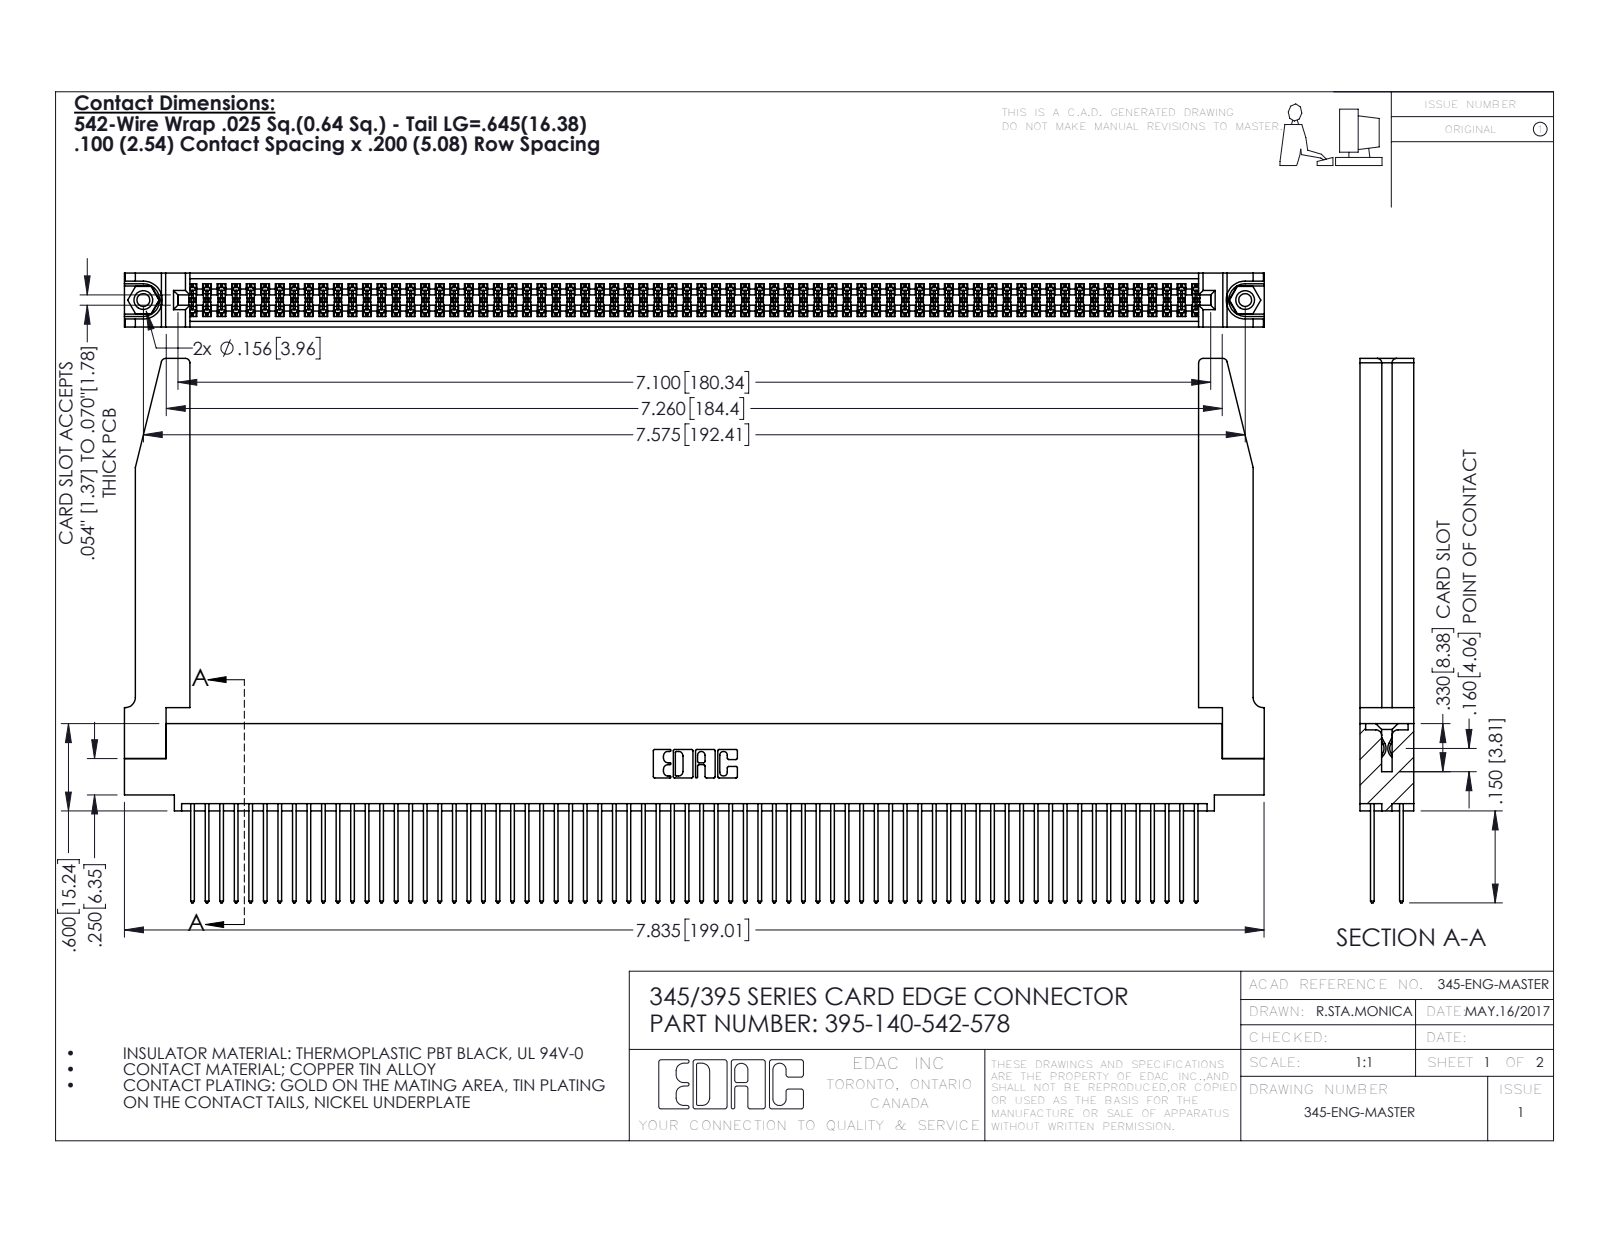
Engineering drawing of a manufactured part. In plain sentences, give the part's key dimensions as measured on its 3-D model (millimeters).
The part is named "345-220-078_345-220-078; 345 Part_0.110 Offset - 0.156 Dia-TH; 345-250-001_345-250-001-102; 345-292-001_345-293-142 (+1 more)". Its 3-D file was written by "SolidWorks 2016 (CONFIG_CONTROL_DESIGN)". It is 145 solids with 7364 faces: 4846 planar, 2466 cylindrical and 52 other. Overall it measures 199 by 95 by 9.4 millimeters. Its volume is 27 940 cubic millimeters and its surface area 40 340 square millimeters. Round holes: 2 of diameter 2.3, 2 of diameter 3.2, 2 of diameter 4, 1 of diameter 1.6. Round bosses or shafts: 2 of diameter 3.9. Partial cylindrical surfaces (rounded edges, fillets, slot ends): 210 of radius 0.2, 140 of radius 0.3, 22 of radius 0.3, 8 of radius 0.8, 6 of radius 0.2, 6 of radius 0.8, 3 of radius 0.7, 2 of radius 0.4. The main face-to-face distances are 1.8, 7.6, 9.4, 5.1, 2.5, 6.9, 0.6, 5.7, 4.4, 3.8. The hole center spacings are 6.9, 186.4, 192.4.
